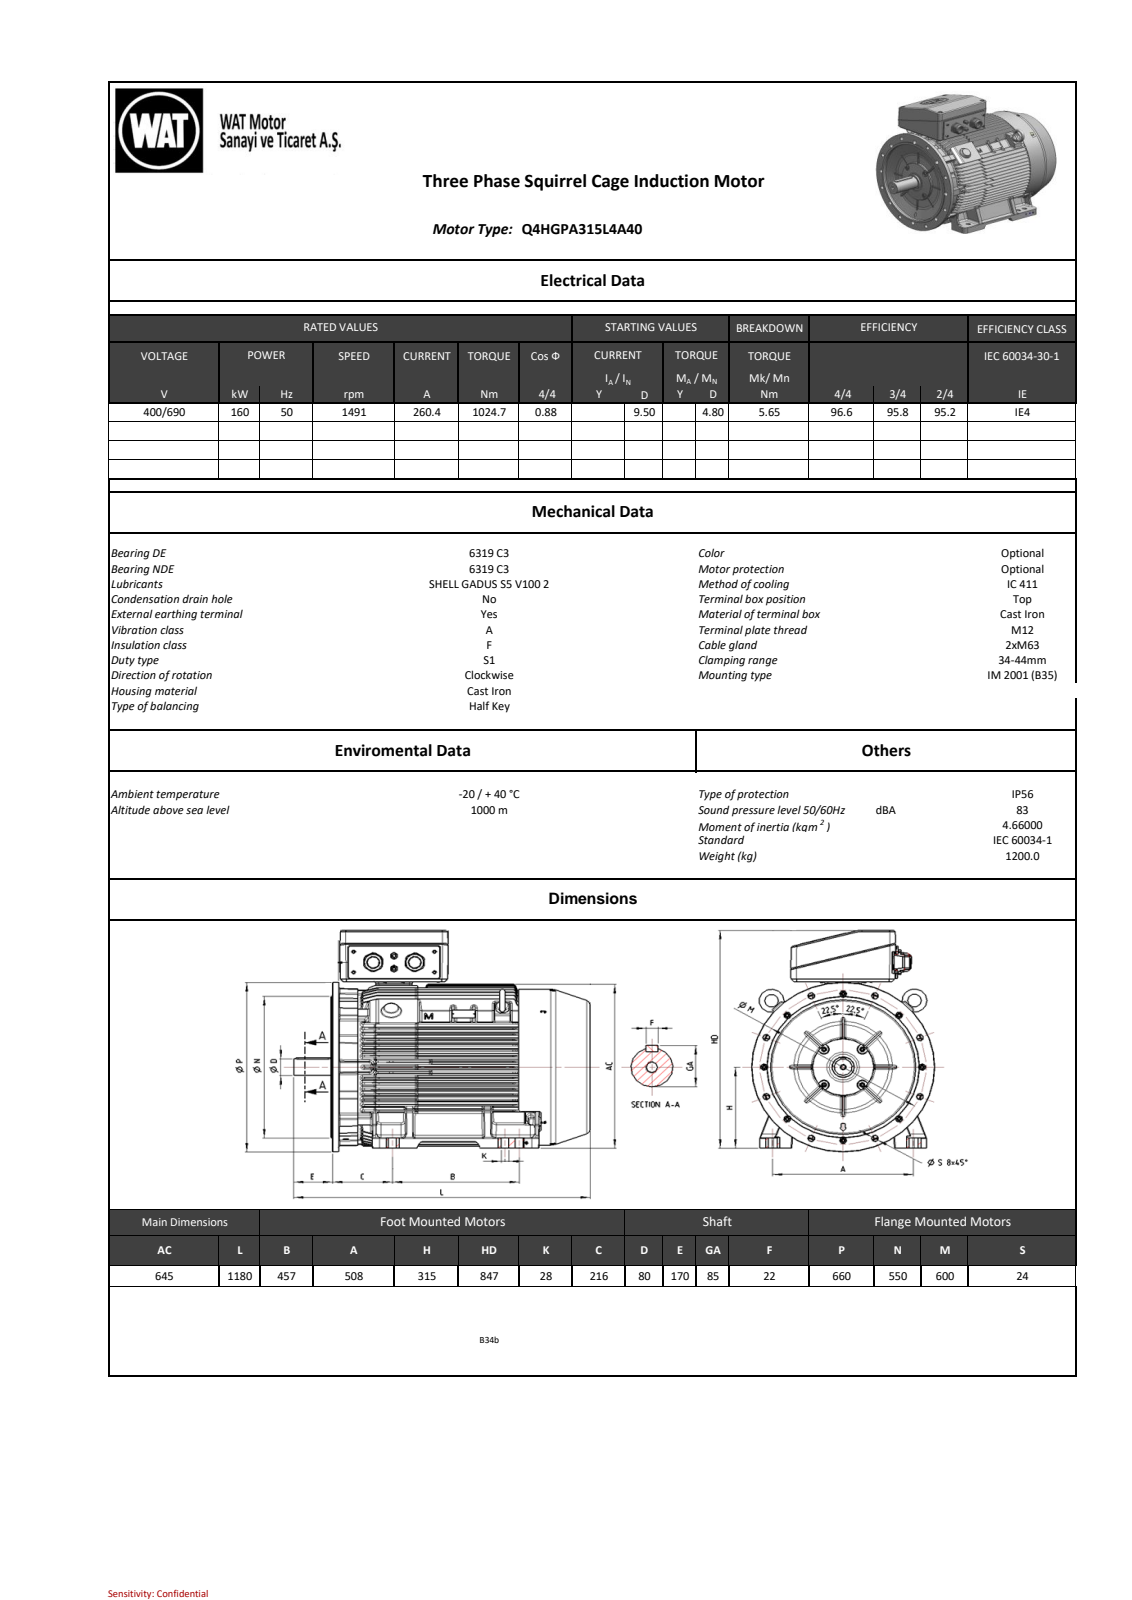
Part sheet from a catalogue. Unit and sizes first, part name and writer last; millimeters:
Units: millimetres
Overall size (bounding box): 1180 × 862.37 × 660
Round holes (diameter × count): ⌀24 ×8, ⌀26 ×8, ⌀20 ×7, ⌀8.5 ×3, ⌀9 ×3, ⌀4 ×2, ⌀12 ×2, ⌀12.1 ×2, ⌀21 ×2, ⌀44 ×2, ⌀44.4 ×2, ⌀44.5 ×2
Round bosses / shafts (diameter × count): ⌀16 ×8, ⌀10 ×8, ⌀20 ×4, ⌀64.8 ×2, ⌀50 ×2, ⌀660 ×1, ⌀607 ×1, ⌀565 ×1
Partial cylindrical surfaces — rounded edges, fillets, slot ends (radius × count): R6 ×616, R3 ×120, R1.5 ×68, R2.09 ×59, R2.61 ×54, R0.8 ×38, R15 ×34, R10 ×24
Main face-to-face distances: 20.8, 263.64, 20.71, 305.15, 242.75, 221.95, 41.69, 20.89, 41.51, 284.35
Hole centre spacings: 486.48, 79.05, 79.06, 150, 115.07, 115.08, 218.13, 300
Bodies: 0 solids, 6471 faces (2745 planar, 1434 cylindrical, 2292 other)
Part name (STEP PRODUCT): 26009910674F4pys
STEP written by: SIEMENS PLM Software NX 11.0 (AUTOMOTIVE_DESIGN)
